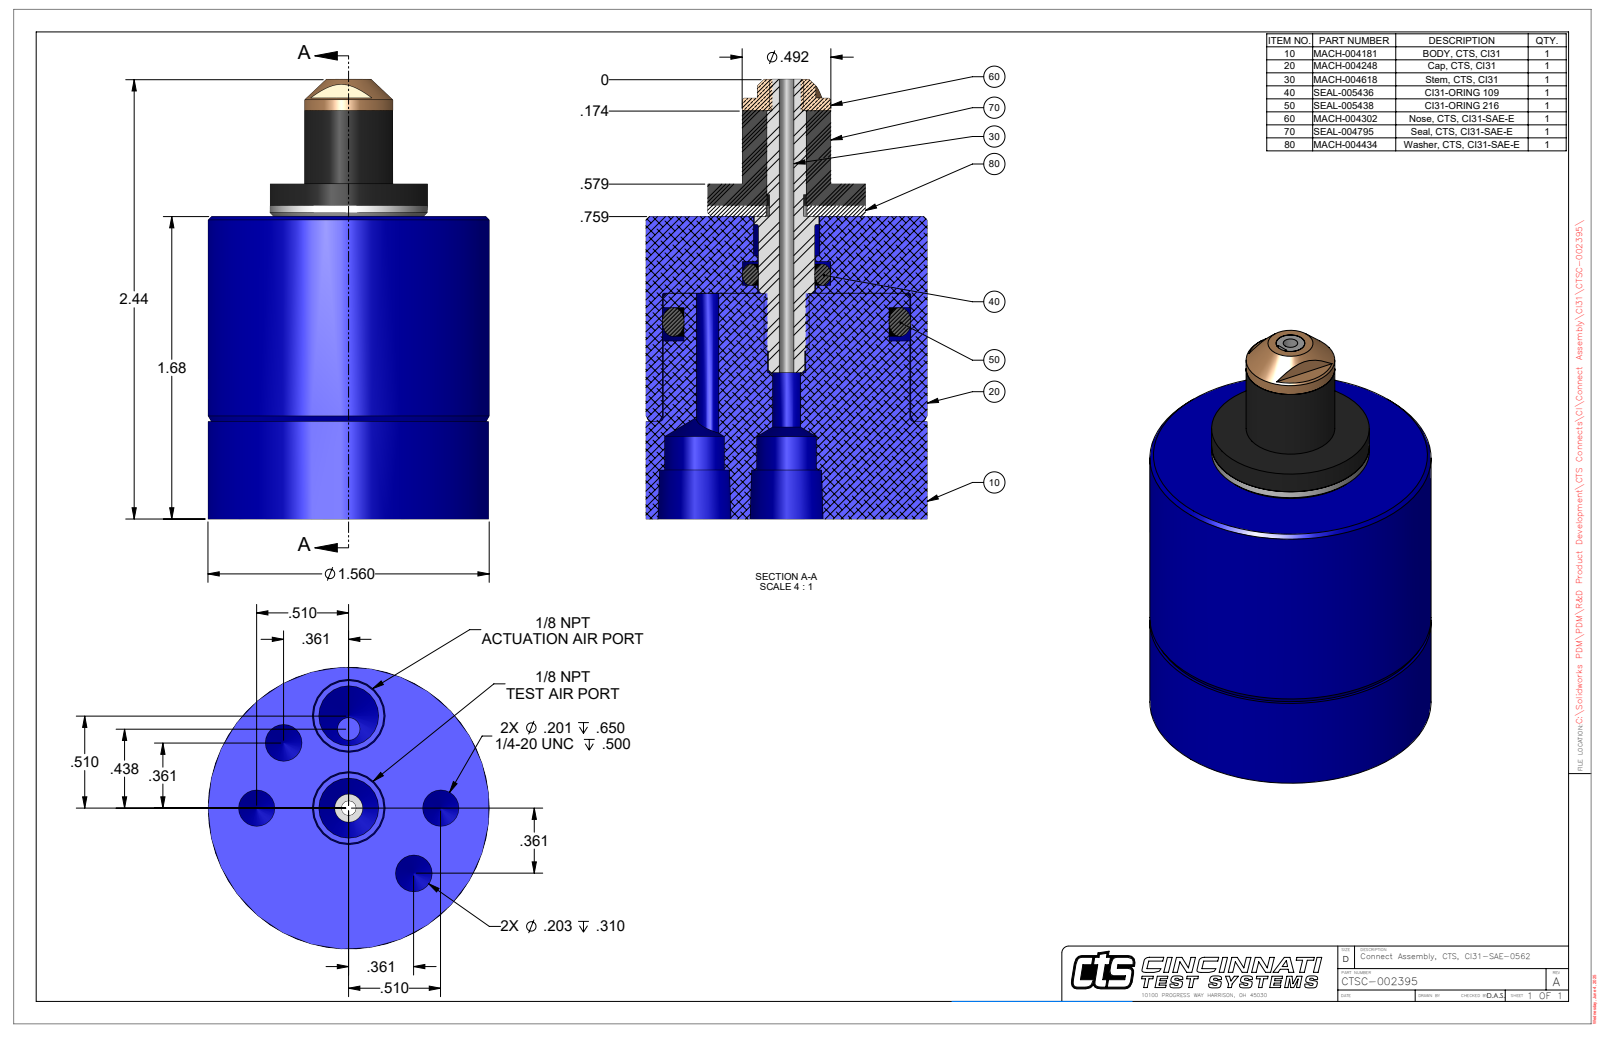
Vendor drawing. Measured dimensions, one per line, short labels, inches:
name: CTSC-002395
written by: SolidWorks 2023 (AUTOMOTIVE_DESIGN)
unit: in
bodies: 1 solid, 87 faces (22 planar, 35 cylindrical, 30 other)
size: 2.437 × 1.56 × 1.56
volume: 3.217 in³; area: 18.91 in²
holes: 2× ⌀0.201, 2× ⌀0.203, 2× ⌀0.332, 1× ⌀0.081, 1× ⌀0.125, 1× ⌀0.156, 1× ⌀0.368, 1× ⌀1.377
bosses: 1× ⌀1.56, 1× ⌀1.365, 1× ⌀0.875, 1× ⌀0.492, 1× ⌀0.357
rounds: 1× R0.079
face distances: 1.677, 1.857, 0.18, 0.542, 1.135, 1.315, 0.812, 0.27, 0.865, 1.045
hole spacings: 0.51, 0.39, 0.942, 0.672, 0.721, 0.072, 0.369, 0.437
